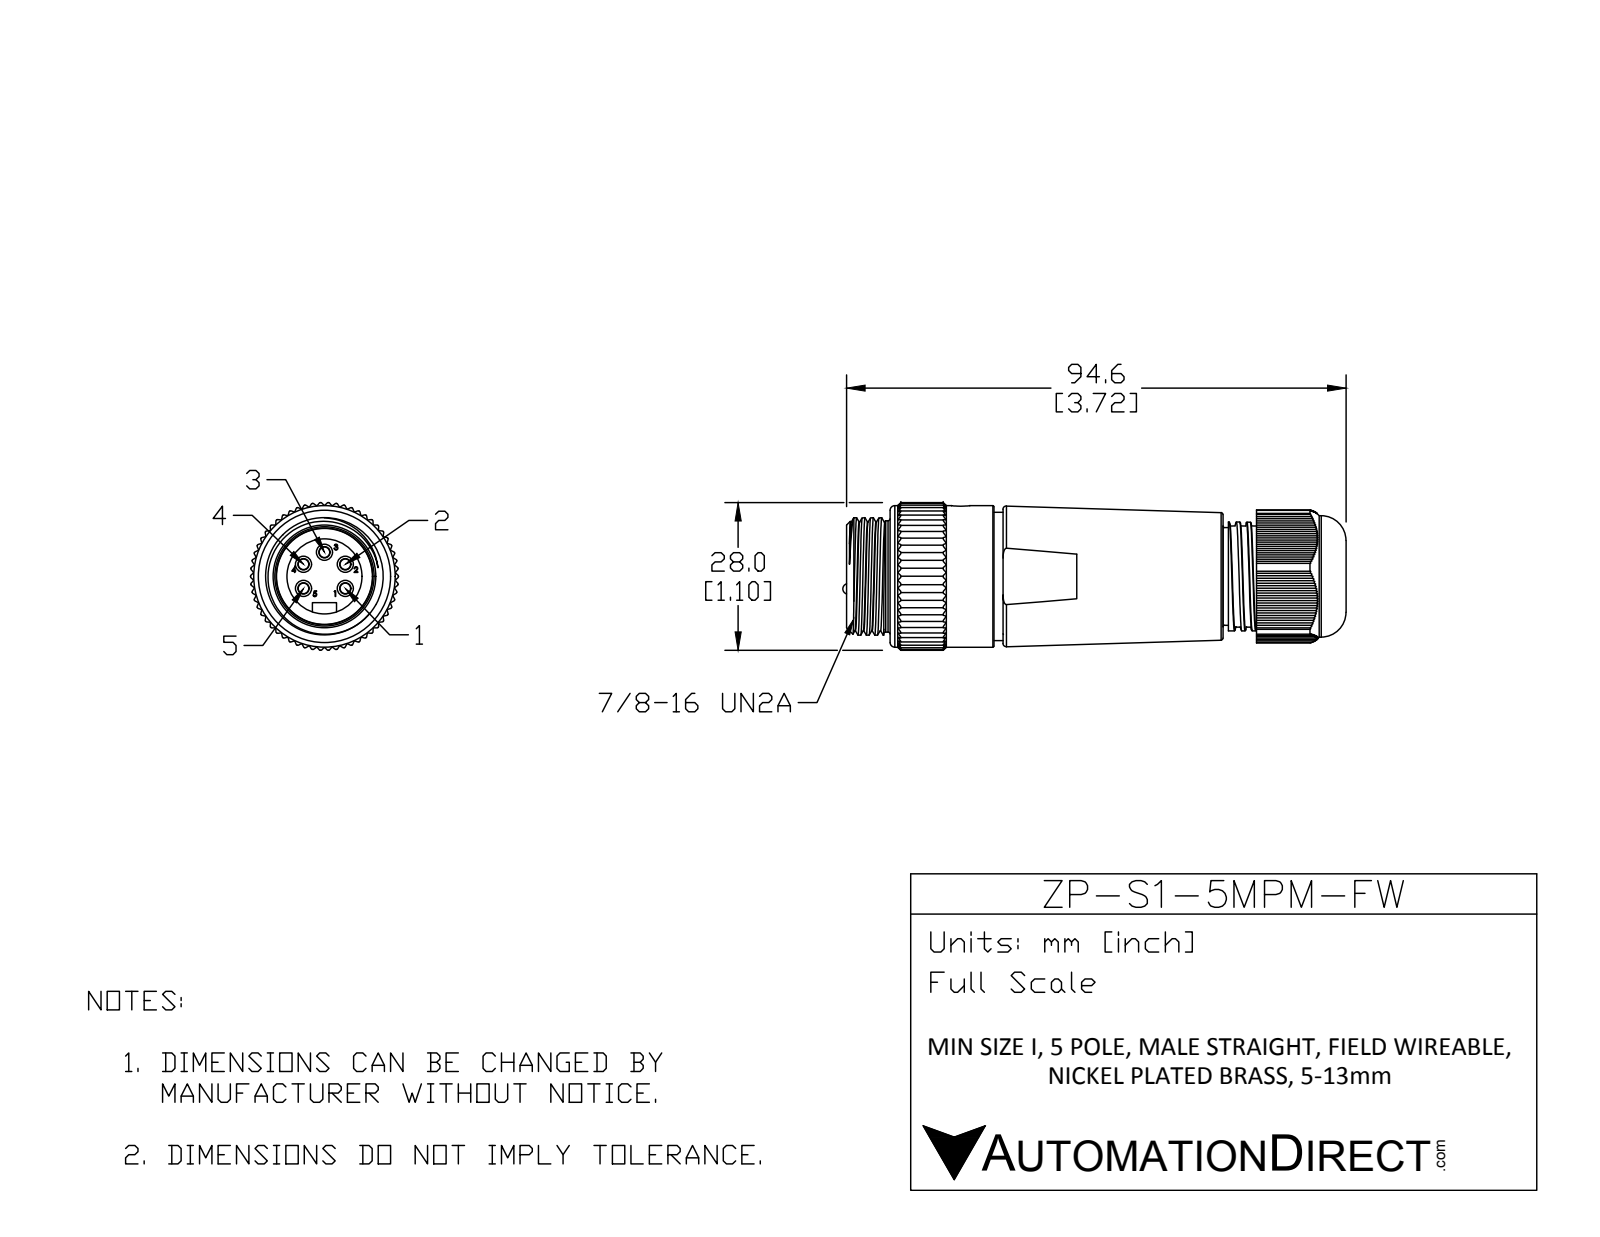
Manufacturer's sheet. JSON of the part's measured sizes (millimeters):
{"part_name": "ZP-S1-5MPM-FW", "step_written_by": "SolidWorks 2015 (AUTOMOTIVE_DESIGN)", "units": "millimeters", "bodies": {"solids": 9, "faces": 878, "planar": 468, "cylindrical": 324, "other": 86}, "overall_size": [94.64, 27.99, 27.98], "volume_mm3": 41367, "surface_area_mm2": 15878, "round_holes": [[3.56, 1], [13.46, 1], [14.22, 1], [18.28, 1], [21.57, 1], [24.2, 1], [25.4, 1]], "round_bosses_or_shafts": [[3.15, 5], [2, 5], [26.8, 1], [24.3, 1], [22.99, 1], [22.22, 1], [20.6, 1], [18.14, 1]], "partial_cylinders_radius": [[0.25, 165], [2.29, 1], [13.23, 1], [14, 1]], "face_to_face_distances": [68.78, 1.06, 0.35, 0.71, 69.78, 6.35, 8.79, 59.99, 1.41, 2.12]}
